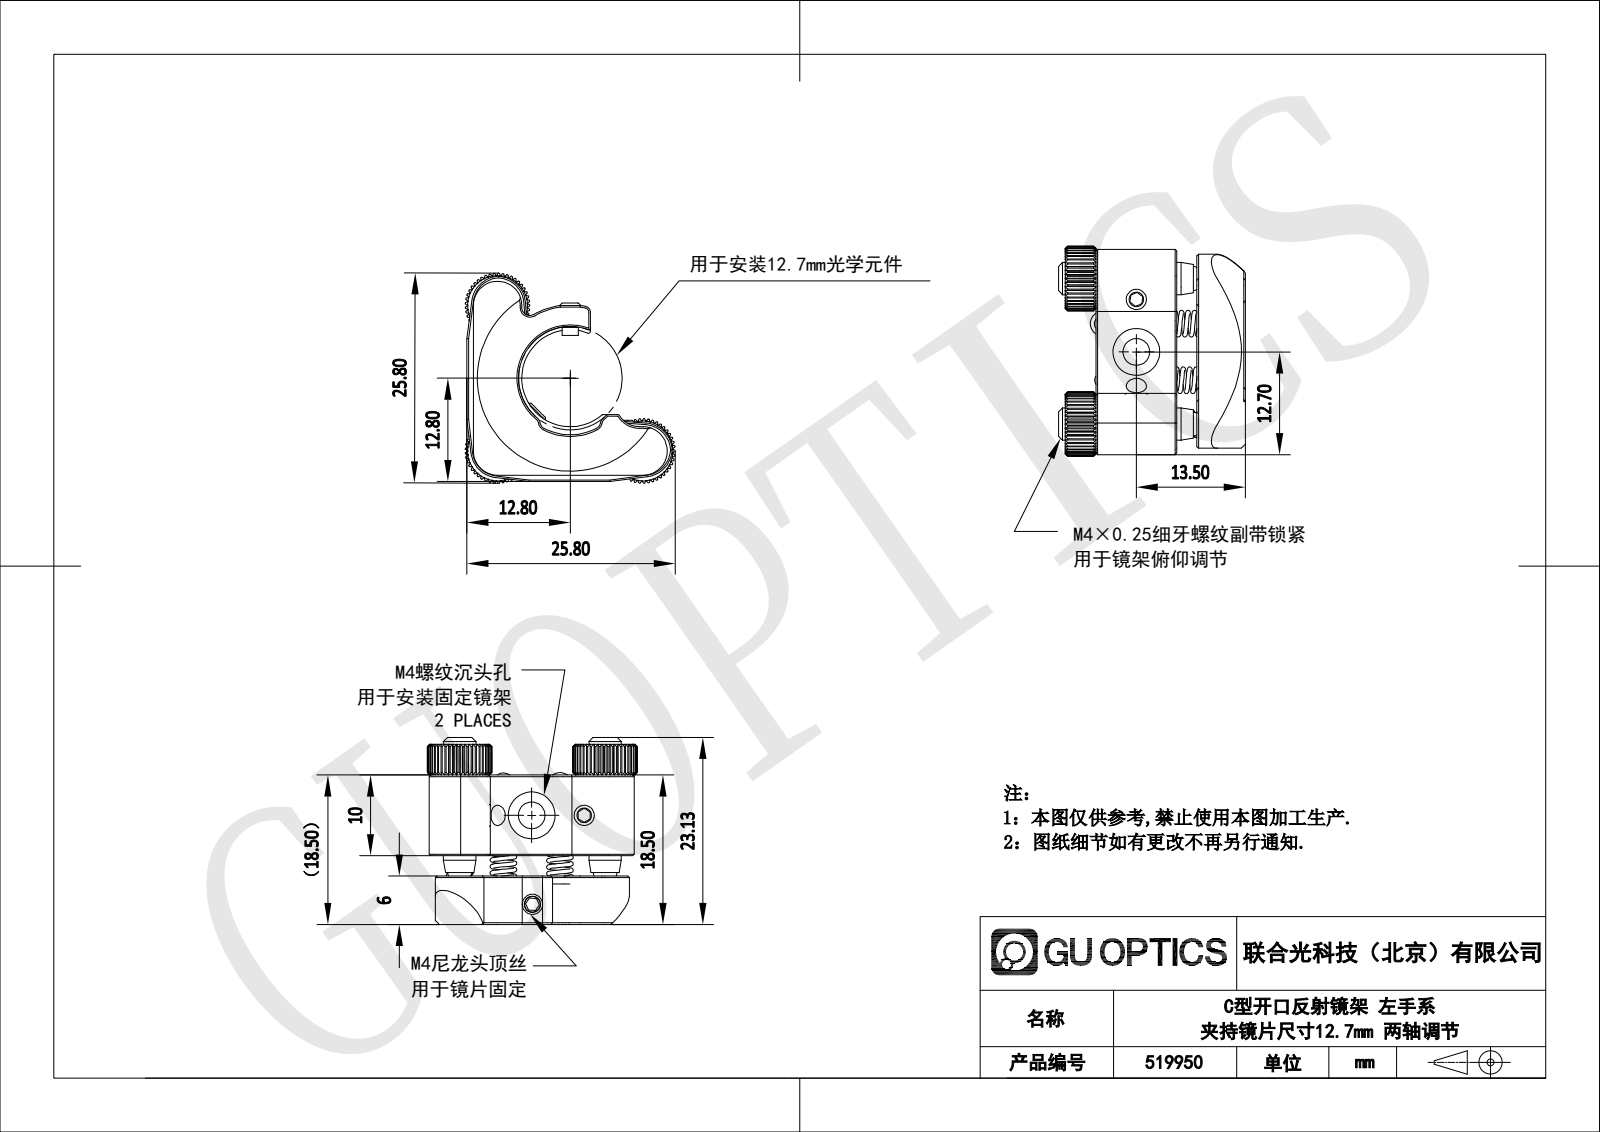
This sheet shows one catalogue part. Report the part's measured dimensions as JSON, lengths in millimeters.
{"step_written_by": "SolidWorks 2021 (CONFIG_CONTROL_DESIGN)", "units": "millimeters", "bodies": {"solids": 0, "faces": 360, "planar": 112, "cylindrical": 109, "other": 139}, "overall_size": [25.2, 25.2, 21.2], "round_holes": [[3.2, 4], [2.8, 3], [5.5, 3], [1.5, 2], [3.3, 2], [6, 2], [2.5, 1], [4.6, 1]], "round_bosses_or_shafts": [[1.5, 5], [5.8, 3], [4, 2], [3, 2], [2, 1]], "partial_cylinders_radius": [[0.75, 11], [0.25, 5], [1, 5], [0.9, 4], [3, 4], [3.5, 3], [5, 2], [6, 1]], "face_to_face_distances": [2.4, 12.4, 10, 6, 8.4, 18.4, 0.7, 5.57, 4.87, 5], "hole_center_spacings": [5.41, 5.59, 7, 12.41, 12.59, 13.54, 18, 18.8]}
